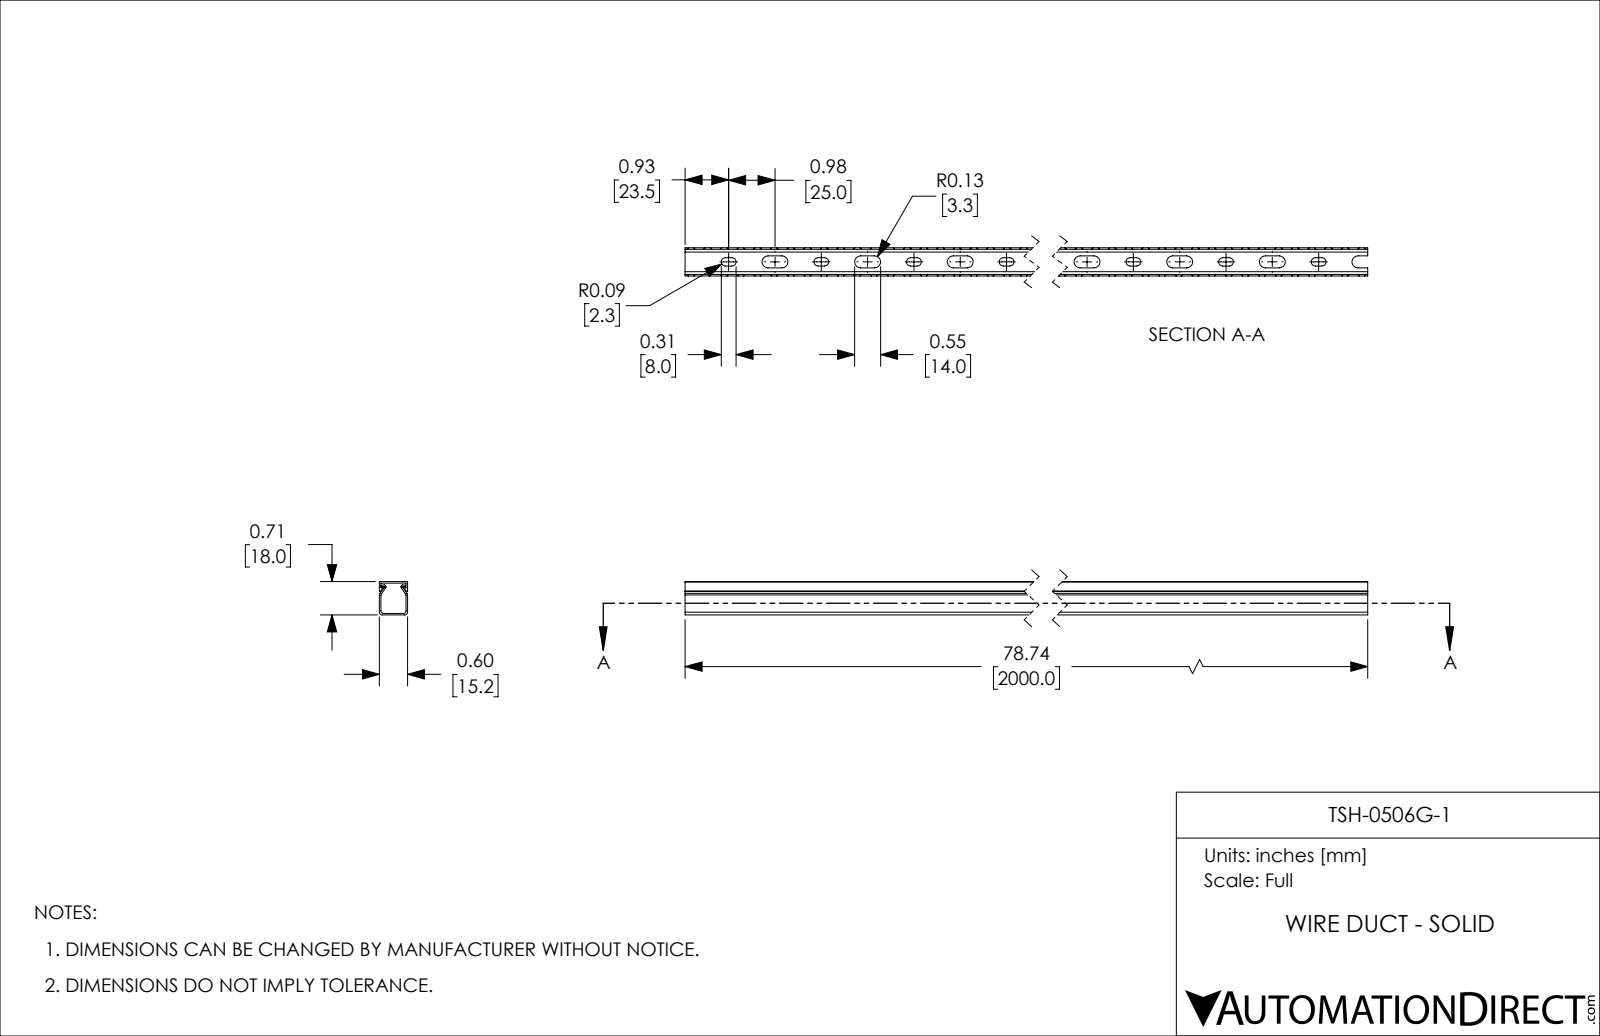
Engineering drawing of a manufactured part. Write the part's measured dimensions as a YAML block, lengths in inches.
part_name: "TSH-0506G-1"
step_written_by: "SolidWorks 2021 (CONFIG_CONTROL_DESIGN)"
units: inches
bodies: {solids: 2, faces: 463, planar: 193, cylindrical: 270, other: 0}
overall_size: [78.74, 0.709, 0.598]
volume: 7.411
surface_area: 464.5
partial_cylinders:
  - {radius: 0.089, count: 80}
  - {radius: 0.128, count: 79}
  - {radius: 0.059, count: 12}
  - {radius: 0.01, count: 10}
  - {radius: 0.015, count: 8}
face_to_face_distances: [0.031, 0.567, 0.677, 0.598, 0.535, 0.709, 0.646, 0.298, 0.33, 0.171]
